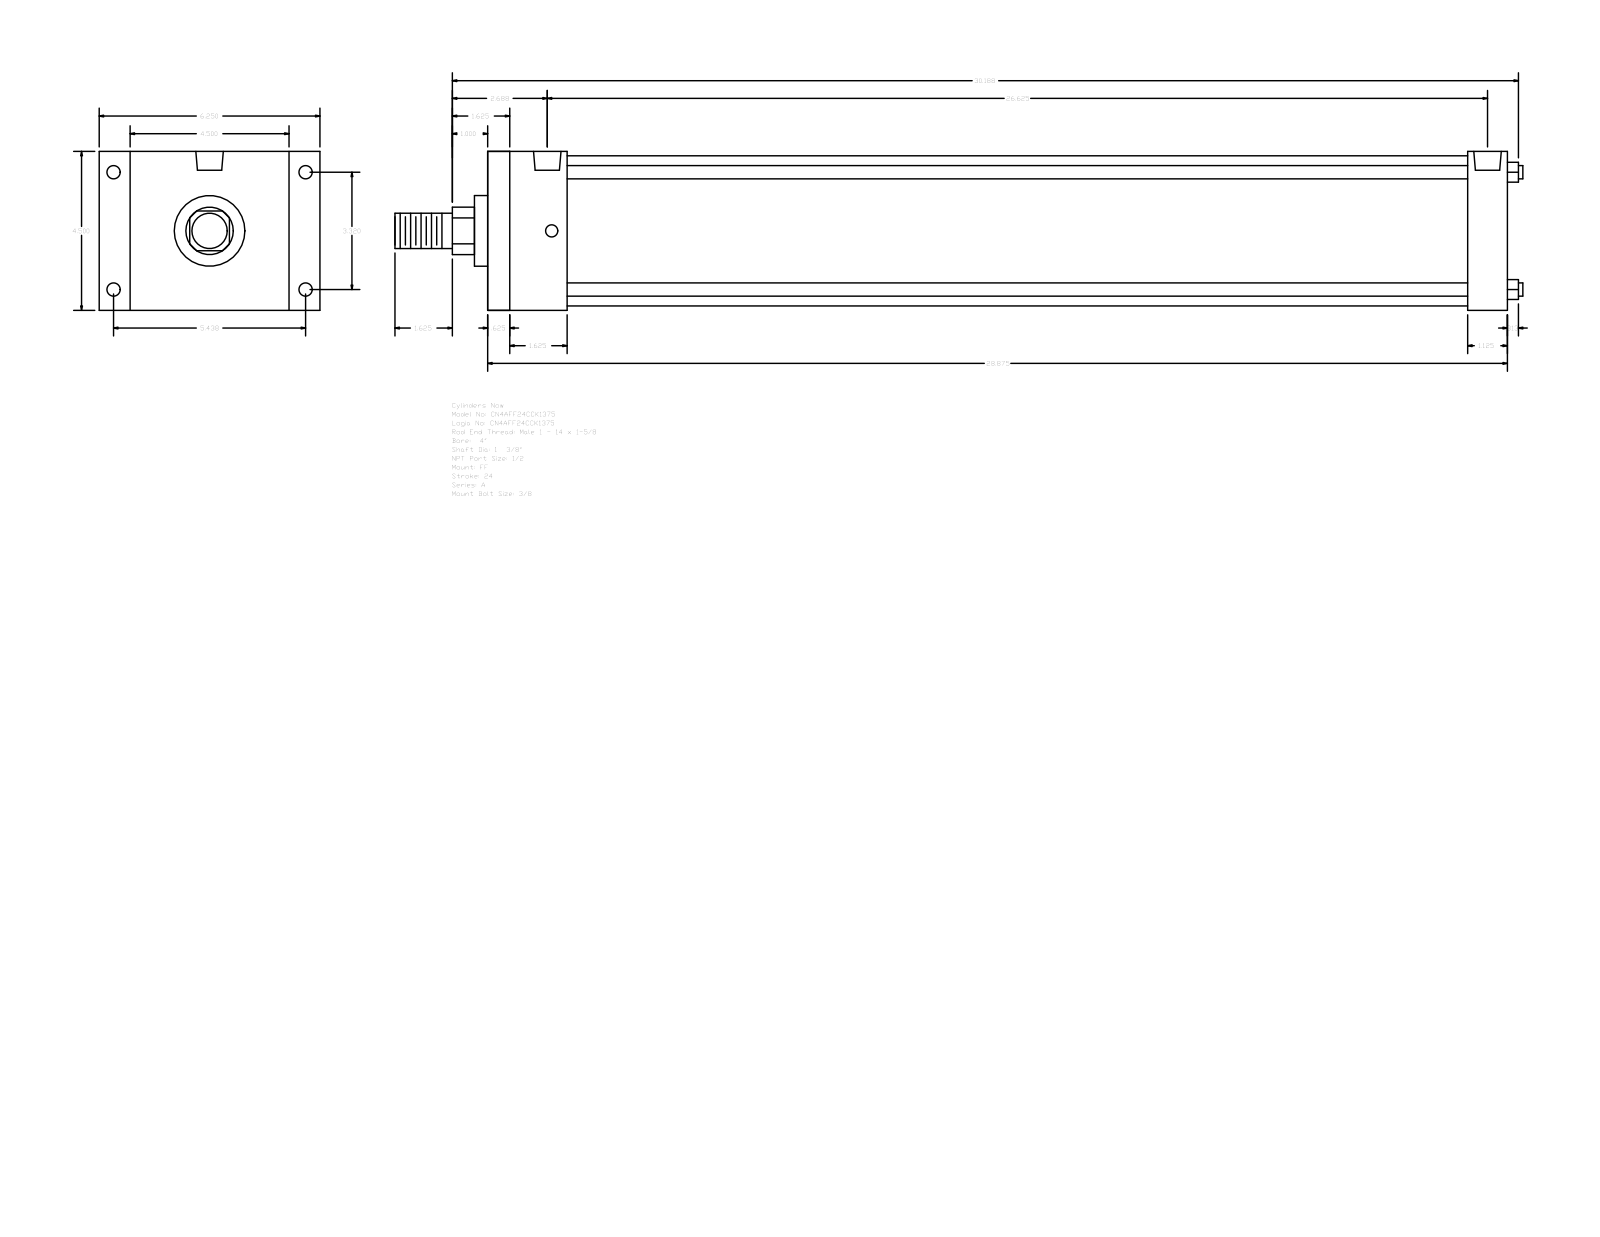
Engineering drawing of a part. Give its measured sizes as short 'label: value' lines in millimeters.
name: A_FF__0400_1.375
written by: GSSL Pune (CONFIG_CONTROL_DESIGN)
unit: mm
bodies: 0 solids, 92 faces (64 planar, 28 cylindrical, 0 other)
size: 811.21 × 158.75 × 114.3
holes: 4× ⌀8.73, 4× ⌀9.53, 2× ⌀19.77
bosses: 4× ⌀9.53, 1× ⌀107.95, 1× ⌀50.8, 1× ⌀34.92, 1× ⌀25.4
rounds: 1× R17.06
face distances: 114.3, 733.43, 15.87, 717.56, 57.15, 28.58, 22.23, 136.53, 704.85, 688.98
hole spacings: 3.18, 84.32, 138.12, 161.82, 669.92, 673.1, 676.28
